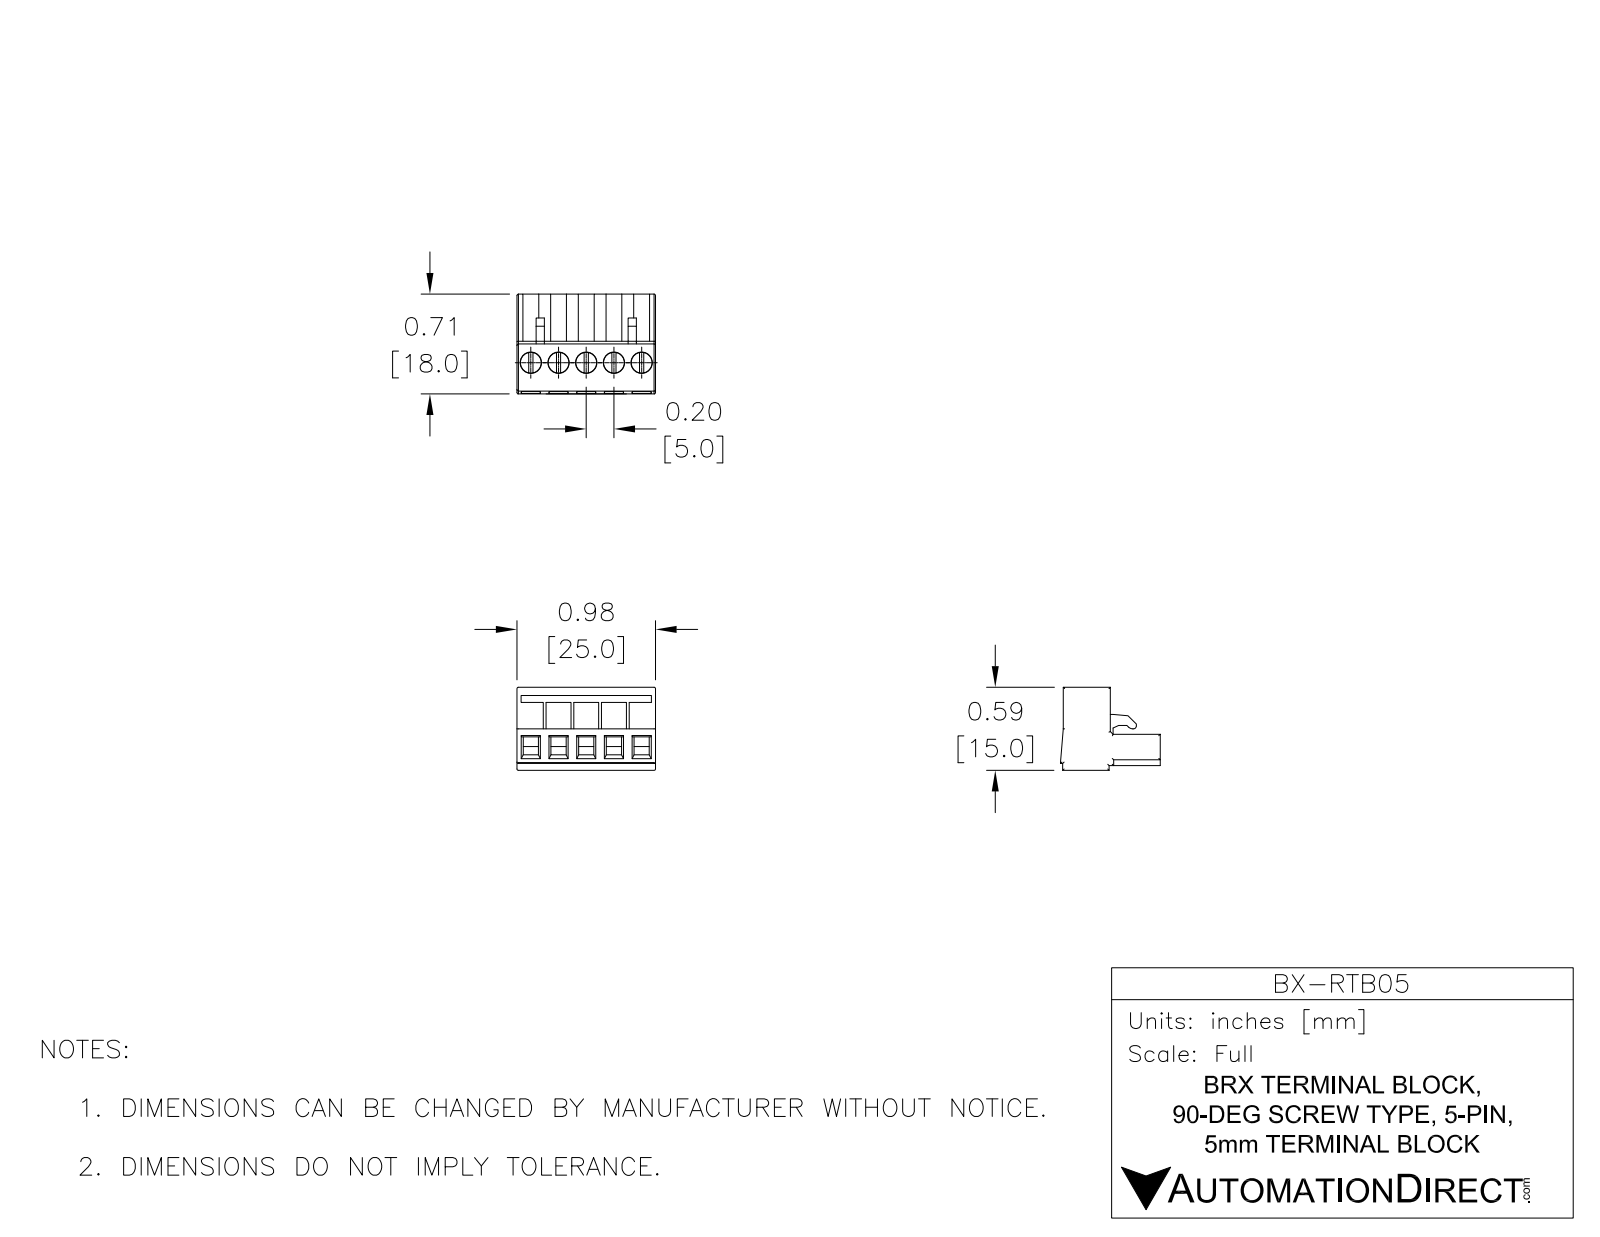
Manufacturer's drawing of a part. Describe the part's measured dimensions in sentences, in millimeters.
The part is named "BX-RTB05". Its 3-D file was written by "SolidWorks 2016 (AUTOMOTIVE_DESIGN)". It is 1 solid with 290 faces: 198 planar, 82 cylindrical and 10 other. Overall it measures 25 by 18 by 15 millimeters. Its volume is 3 820 cubic millimeters and its surface area 3 053 square millimeters. Round holes: 5 of diameter 1.6, 5 of diameter 3.15, 5 of diameter 3.85. Round bosses or shafts: 5 of diameter 3.75. Partial cylindrical surfaces (rounded edges, fillets, slot ends): 29 of radius 0.25, 5 of radius 2.53, 1 of radius 0.5, 1 of radius 1. The main face-to-face distances are 8.5, 15, 25, 5.7, 9.3, 6.5, 9, 0.8, 9.85, 17.5. The hole center spacings are 5, 10, 15, 20.
